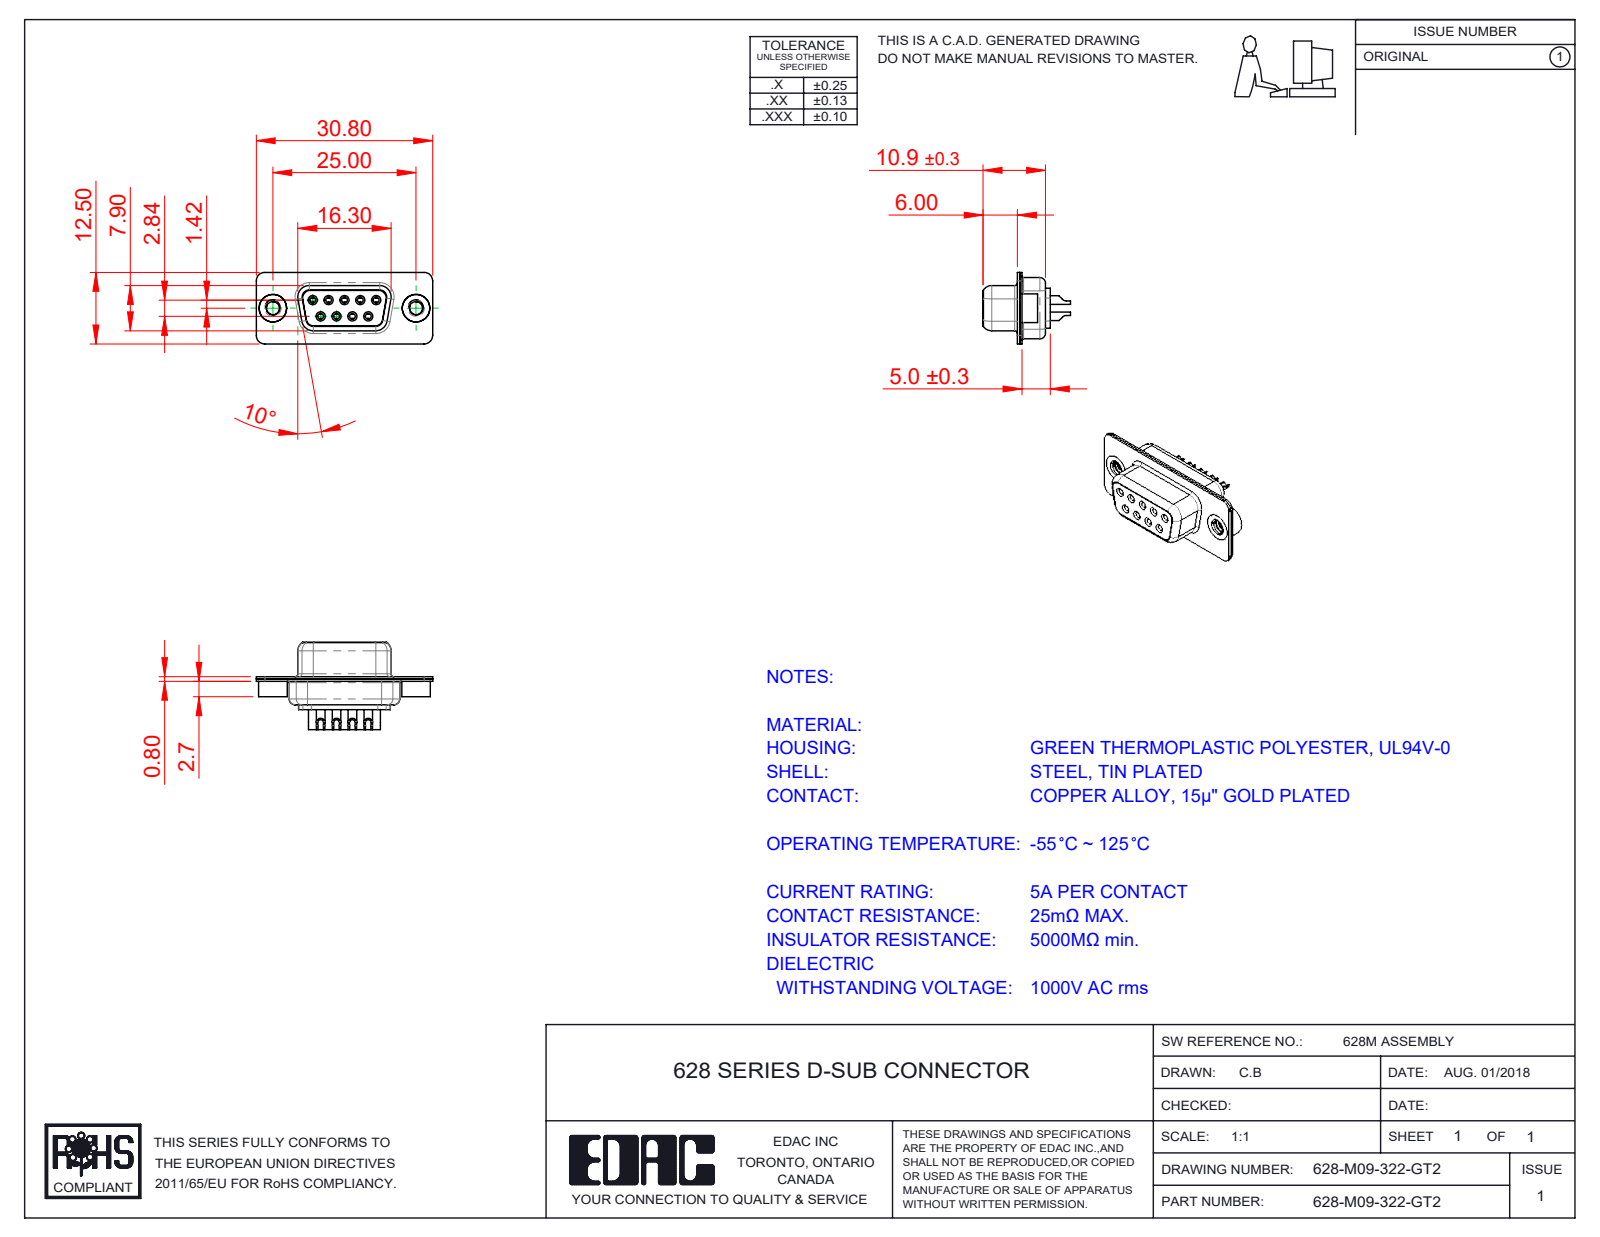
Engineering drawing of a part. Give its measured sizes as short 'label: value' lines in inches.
name: 628M Shell Rear_09 Contacts; 628M Contact Row 1_22; 628-M09-322-GT2; 628M Contact Row 2_22 (+3 more)
written by: SolidWorks 2020 (CONFIG_CONTROL_DESIGN)
unit: in
bodies: 14 solids, 775 faces (221 planar, 326 cylindrical, 228 other)
size: 1.213 × 0.6 × 0.492
volume: 0.105 in³; area: 6.983 in²
holes: 9× ⌀0.039, 9× ⌀0.043, 9× ⌀0.067, 9× ⌀0.071, 9× ⌀0.079, 2× ⌀0.089, 2× ⌀0.157, 2× ⌀0.189
bosses: 9× ⌀0.087, 9× ⌀0.063, 9× ⌀0.059, 2× ⌀0.197, 2× ⌀0.193
rounds: 16× R0.059, 12× R0.079, 8× R0.053, 8× R0.063, 6× R0.039, 4× R0.01, 4× R0.02, 4× R0.024
face distances: 0.016, 0.055, 0.018, 0.333, 0.031, 0.35, 0.071, 0.039, 0.278, 0.033
hole spacings: 0.124, 0.109, 0.218, 0.198, 0.198, 0.327, 0.28, 0.294
